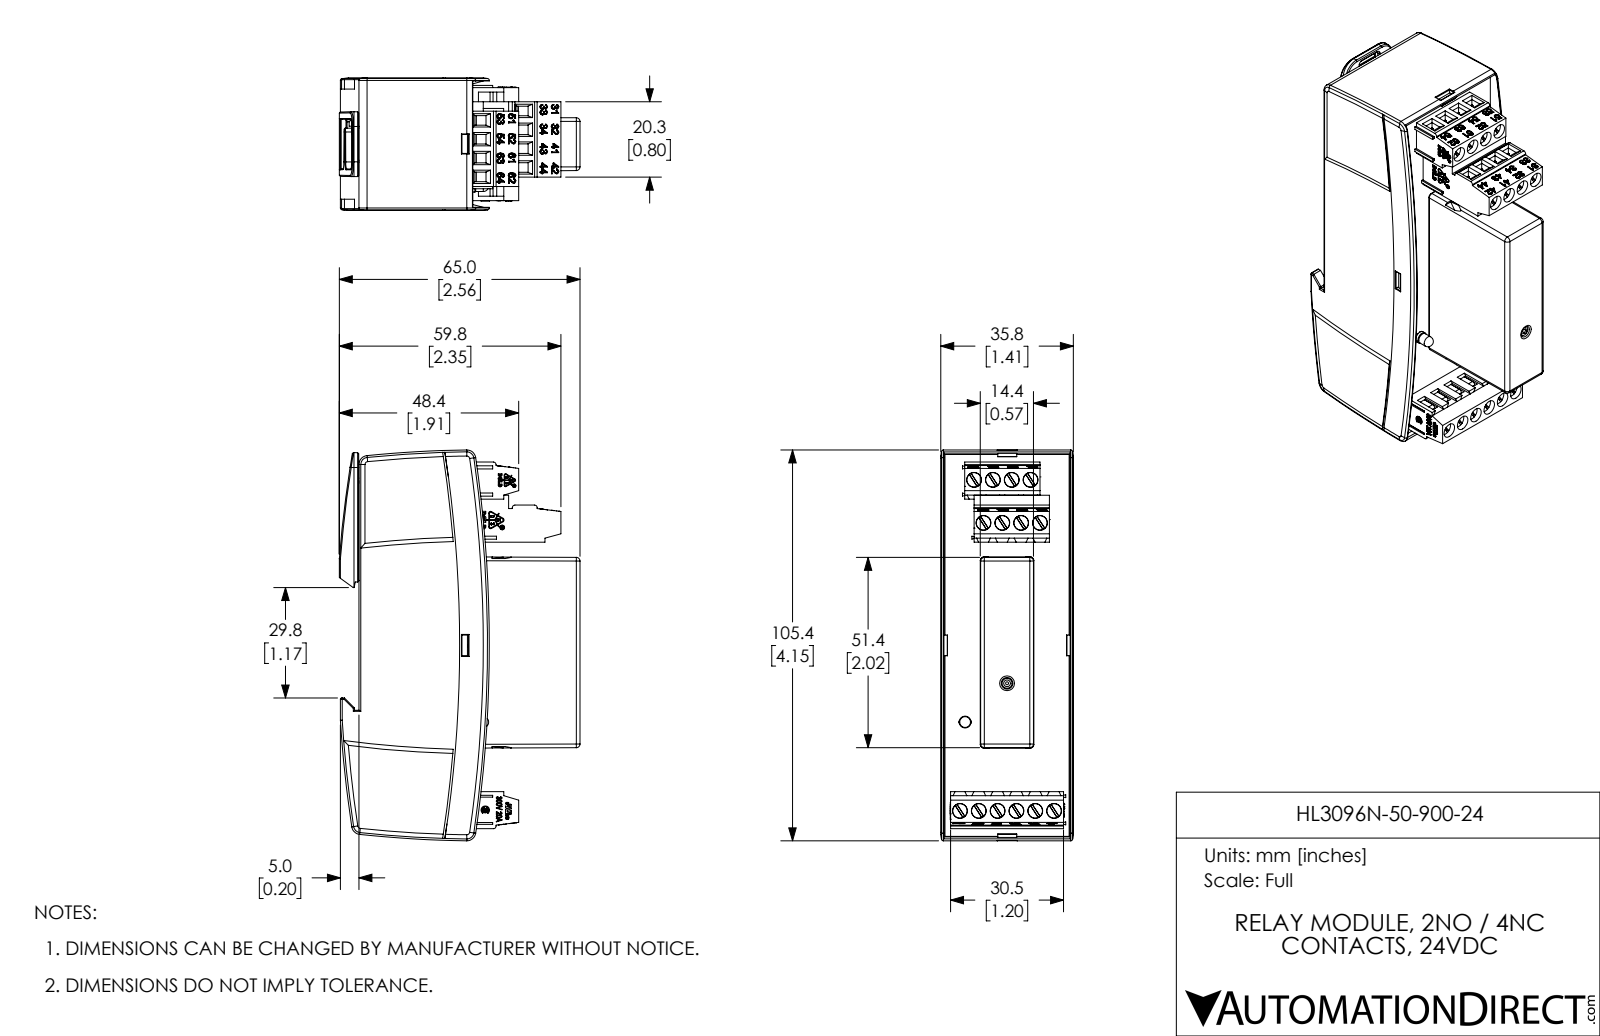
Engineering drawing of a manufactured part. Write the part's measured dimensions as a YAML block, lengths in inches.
part_name: "HL3096N-50-900-24"
step_written_by: "SolidWorks 2017 (AUTOMOTIVE_DESIGN)"
units: inches
bodies: {solids: 1, faces: 3802, planar: 2495, cylindrical: 609, other: 698}
overall_size: [4.15, 2.557, 1.409]
volume: 8.974
surface_area: 50.77
round_holes:
  - {diameter: 0.059, count: 27}
  - {diameter: 0.157, count: 14}
  - {diameter: 0.022, count: 2}
  - {diameter: 0.035, count: 2}
  - {diameter: 0.019, count: 1}
  - {diameter: 0.034, count: 1}
  - {diameter: 0.037, count: 1}
  - {diameter: 0.05, count: 1}
  - {diameter: 0.06, count: 1}
round_bosses_or_shafts:
  - {diameter: 0.154, count: 14}
  - {diameter: 0.019, count: 2}
  - {diameter: 0.126, count: 1}
  - {diameter: 0.114, count: 1}
  - {diameter: 0.046, count: 1}
  - {diameter: 0.037, count: 1}
  - {diameter: 0.034, count: 1}
  - {diameter: 0.031, count: 1}
partial_cylinders:
  - {radius: 0.006, count: 48}
  - {radius: 0.02, count: 23}
  - {radius: 0.008, count: 21}
  - {radius: 0.012, count: 15}
  - {radius: 0.039, count: 10}
  - {radius: 0.004, count: 7}
  - {radius: 0.005, count: 6}
  - {radius: 0.005, count: 6}
face_to_face_distances: [1.402, 1.154, 0.026, 1.409, 1.394, 1.376, 0.033, 1.368, 1.195, 1.343]
hole_center_spacings: [0.394, 0.2, 0.197, 0.44, 0.4, 0.557, 0.467, 0.591]
